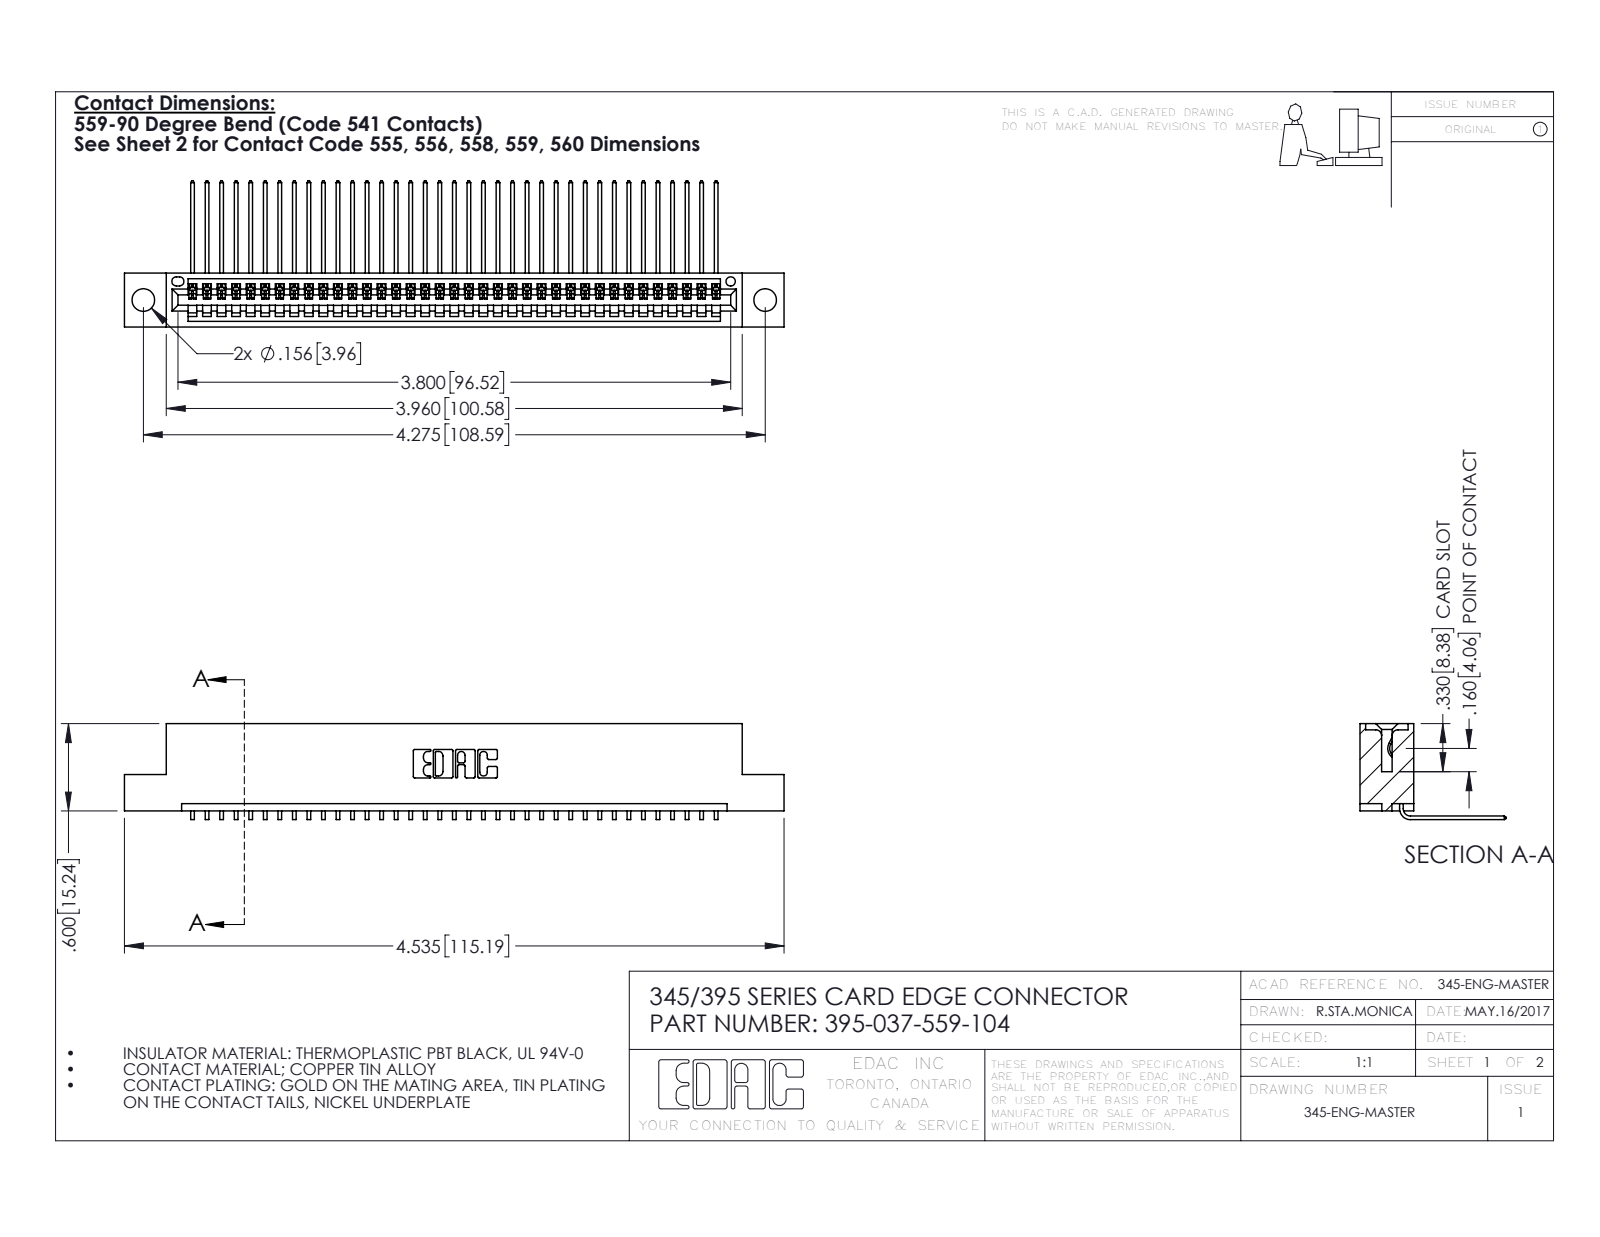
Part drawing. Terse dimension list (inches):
name: 345-292-001_558 559 Tail - 1; 345 Part_Flush Mounting Lugs - 0.156 Dia-TH; 395-037-559-104
written by: SolidWorks 2016 (CONFIG_CONTROL_DESIGN)
unit: in
bodies: 38 solids, 2346 faces (1634 planar, 712 cylindrical, 0 other)
size: 4.535 × 1.005 × 0.659
volume: 0.667 in³; area: 23.25 in²
holes: 2× ⌀0.156, 1× ⌀0.064
rounds: 74× R0.006, 22× R0.01, 6× R0.007, 6× R0.031, 3× R0.026, 2× R0.031, 2× R0.04, 1× R0.014
face distances: 0.298, 0.072, 0.37, 0.2, 0.098, 0.272, 0.025, 0.225, 0.149, 0.072
hole spacings: 0.27, 4.039, 4.275
